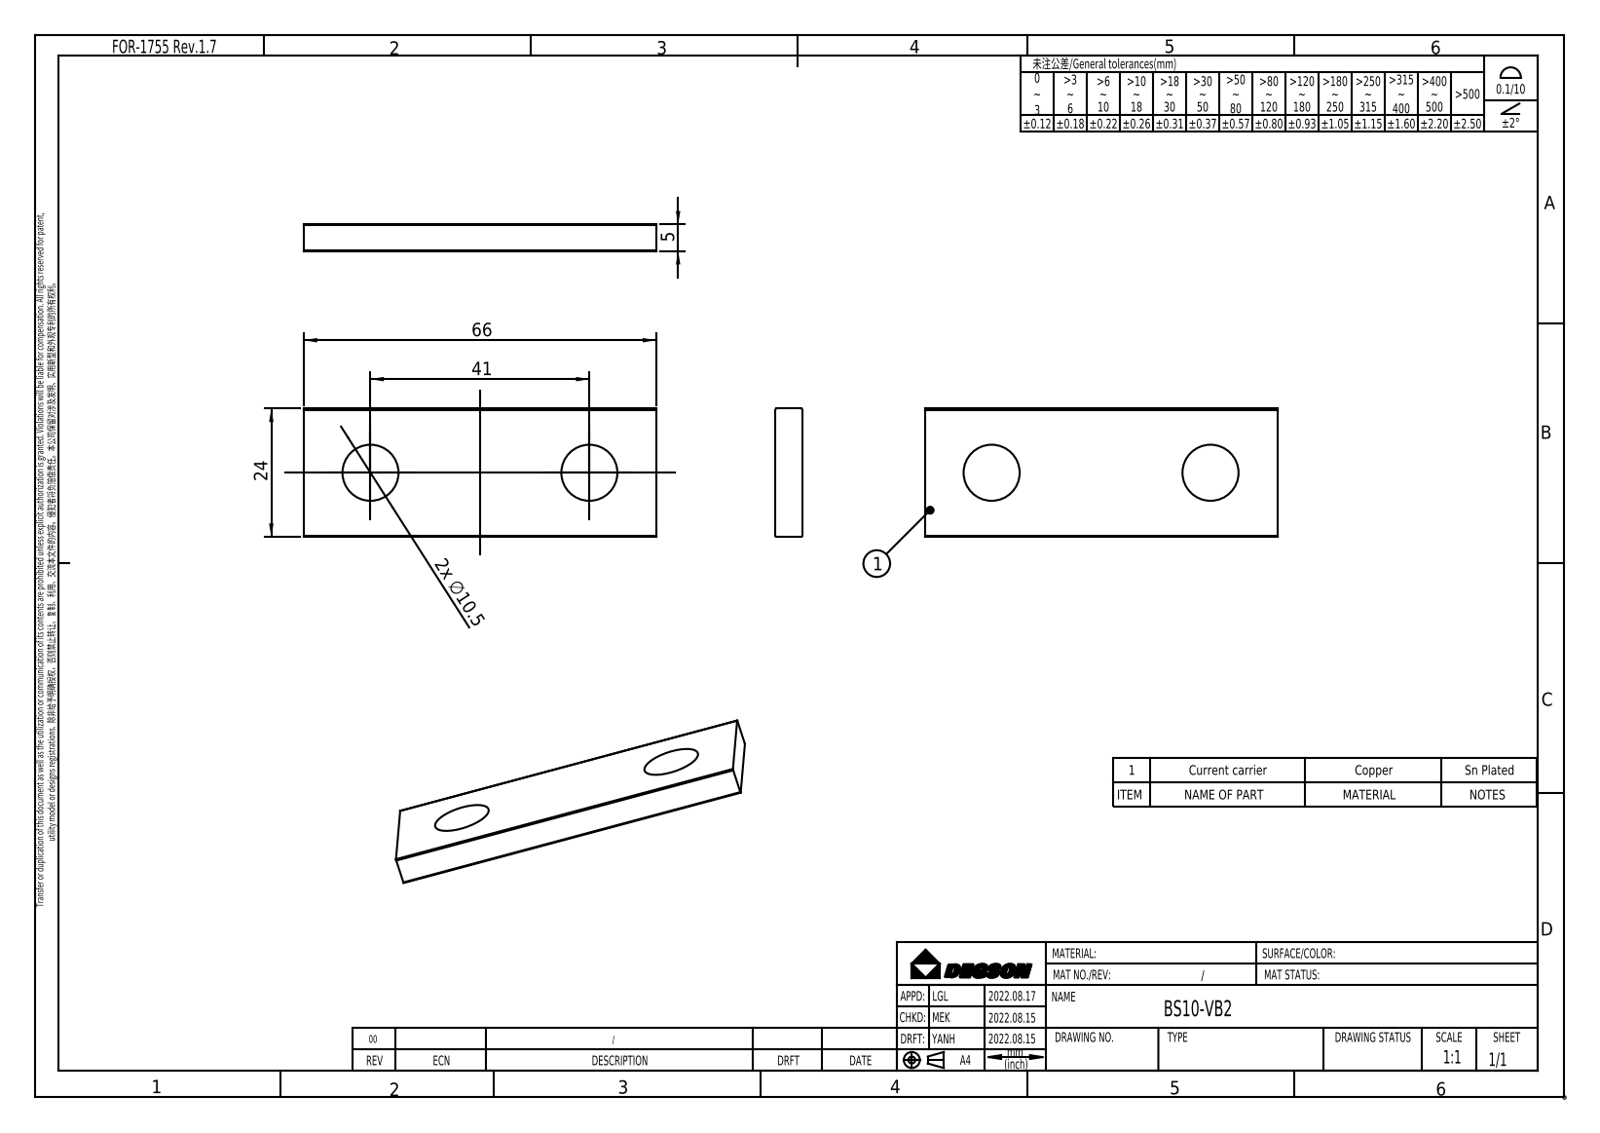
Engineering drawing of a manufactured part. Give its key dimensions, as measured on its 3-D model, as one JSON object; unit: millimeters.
{"part_name": "200076558", "step_written_by": "Solid Edge (AUTOMOTIVE_DESIGN)", "units": "millimeters", "bodies": {"solids": 1, "faces": 12, "planar": 6, "cylindrical": 6, "other": 0}, "overall_size": [66, 24, 5], "volume_mm3": 7052, "surface_area_mm2": 4029, "round_holes": [[10.5, 2]], "partial_cylinders_radius": [[0.2, 4]], "face_to_face_distances": [5, 24, 66], "hole_center_spacings": [41]}
